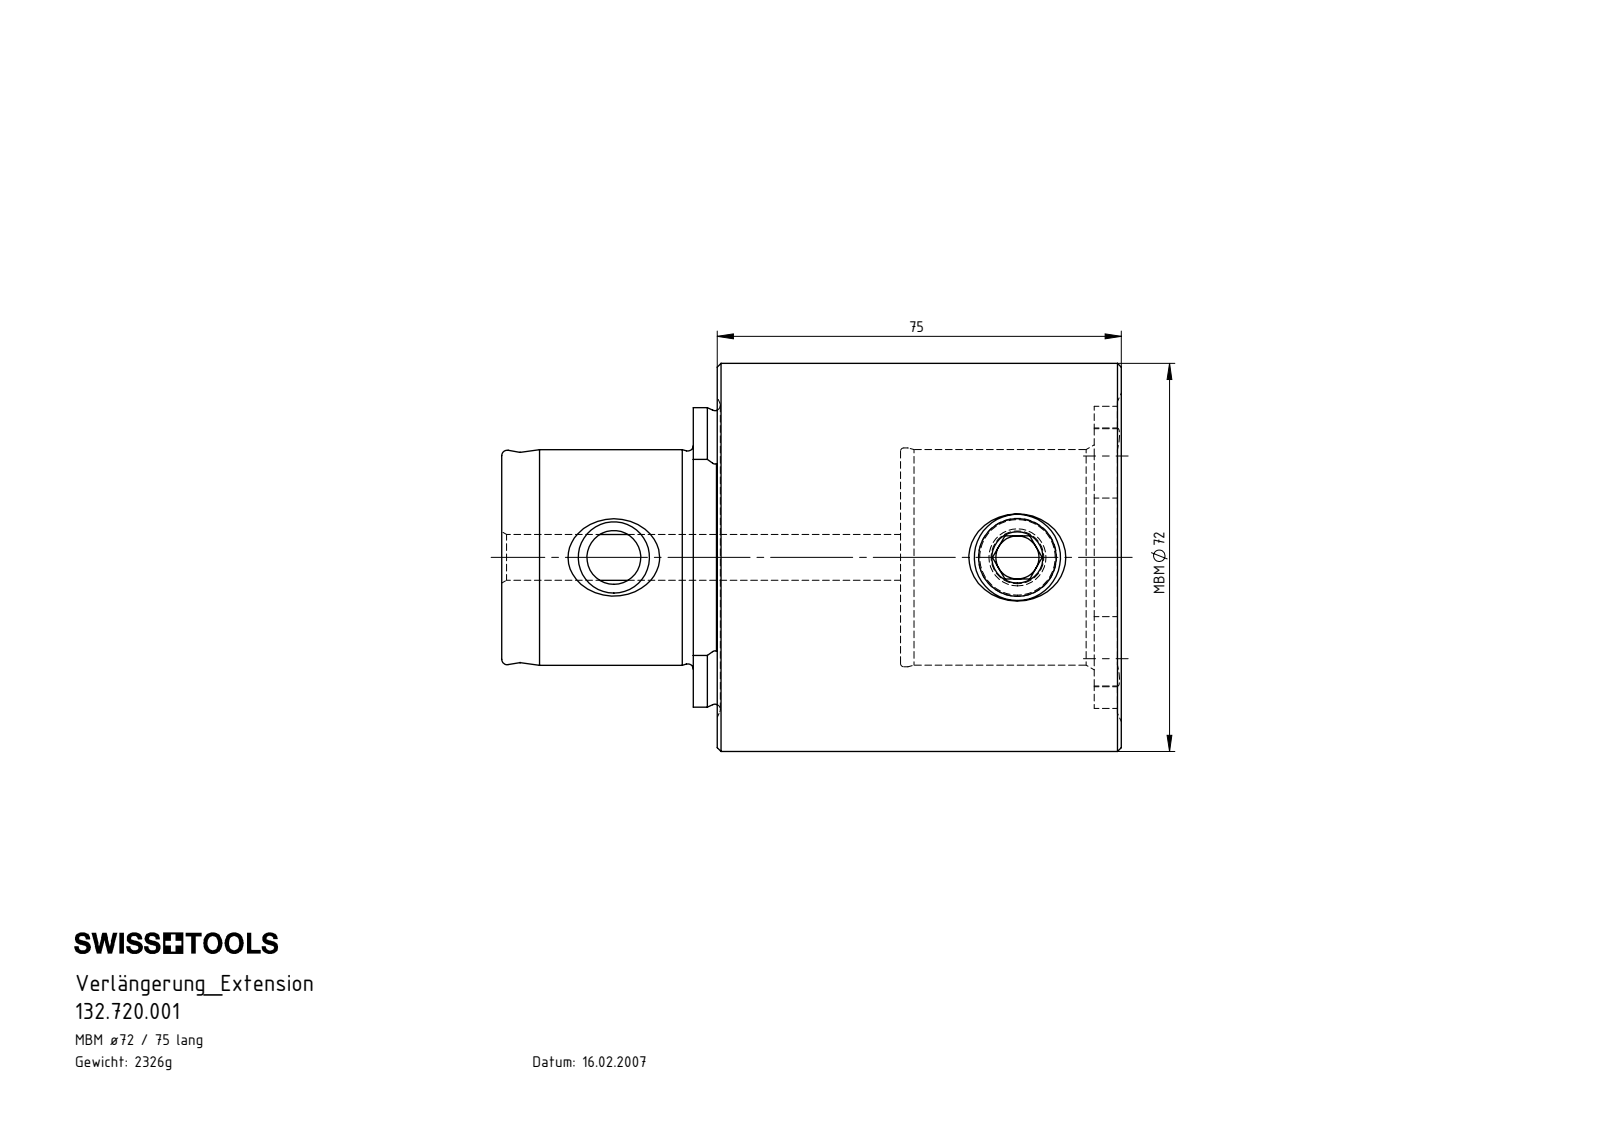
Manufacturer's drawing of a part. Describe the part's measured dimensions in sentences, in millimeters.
The part is named "MB7.MB7.K01.075; MB7-ER1.001.022_A; MB7-MB7.K01.075_B". Its 3-D file was written by "SolidWorks 2011 (CONFIG_CONTROL_DESIGN)". It is 2 solids with 118 faces: 28 planar, 31 cylindrical and 59 other. Overall it measures 115 by 72 by 72 millimeters. Its volume is 296 523 cubic millimeters and its surface area 39 585 square millimeters. Round holes: 1 of diameter 8.5, 1 of diameter 10, 1 of diameter 14.5, 1 of diameter 40, 1 of diameter 40.6. Round bosses or shafts: 1 of diameter 72, 1 of diameter 16. Partial cylindrical surfaces (rounded edges, fillets, slot ends): 4 of radius 5.2, 1 of radius 23.75, 1 of radius 27.77, 1 of radius 28.02. The main face-to-face distances are 34, 40, 74, 115, 75, 41, 74.4, 109.95, 69.95, 35.95. The hole center spacings are 74.65.
